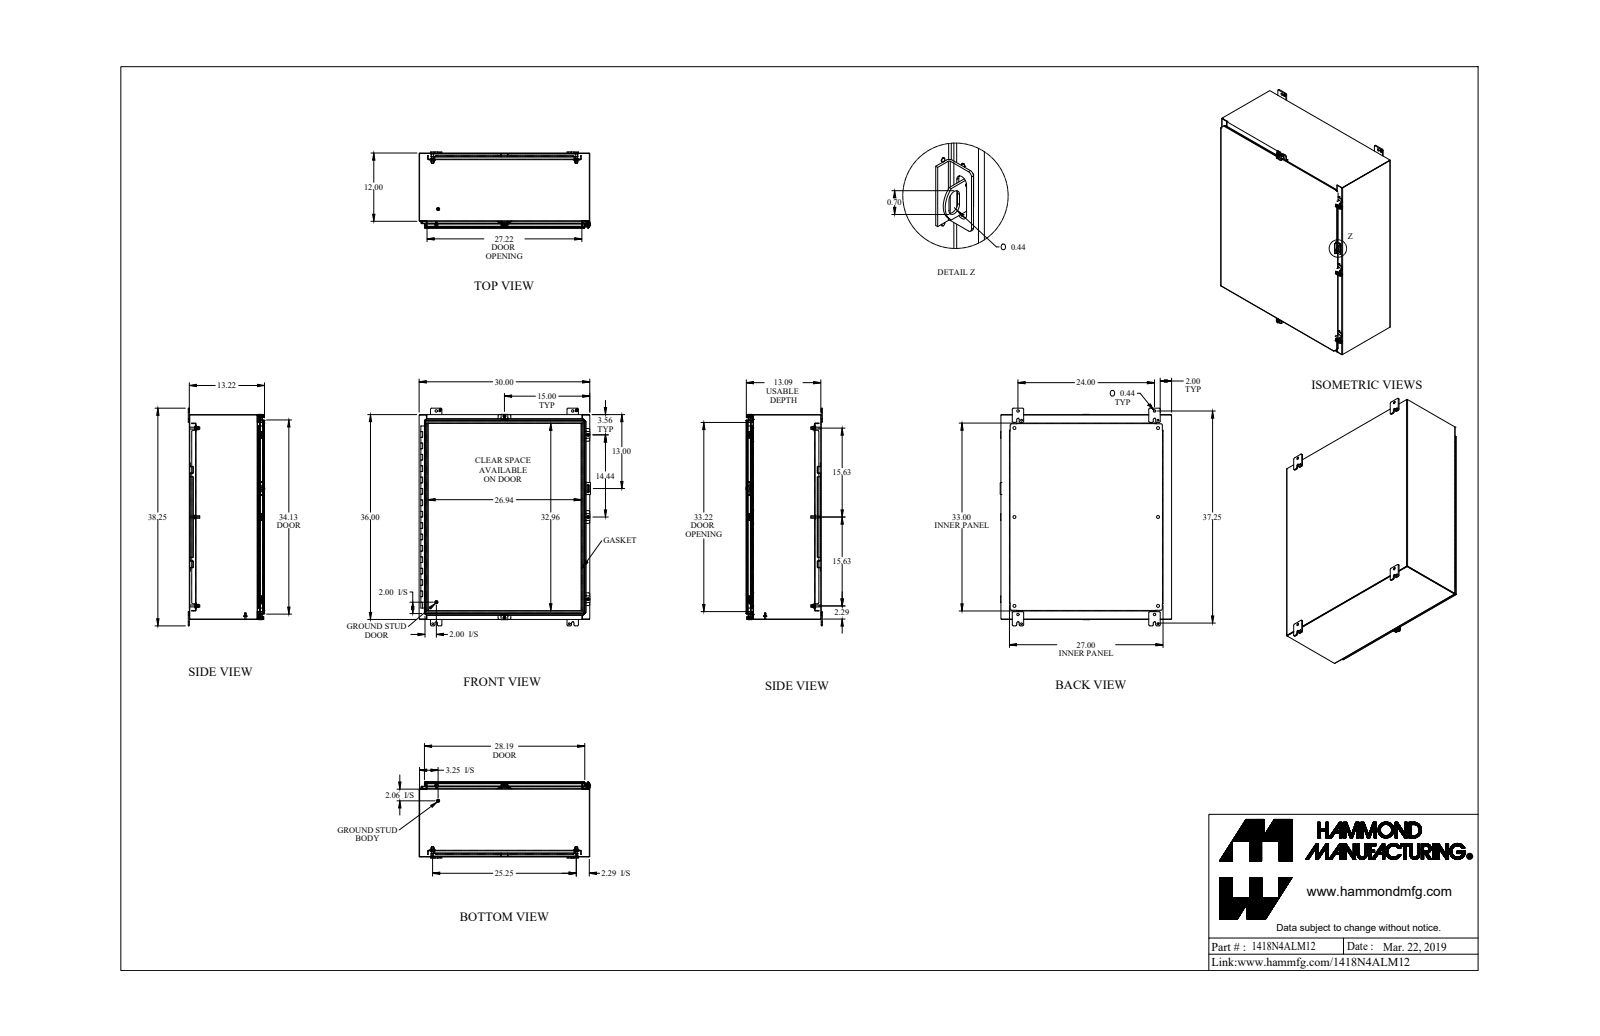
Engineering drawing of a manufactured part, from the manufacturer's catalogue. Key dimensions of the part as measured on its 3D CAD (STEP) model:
Part name (STEP PRODUCT): 1418N4ALM12_Default
STEP written by: SolidWorks 2019 (CONFIG_CONTROL_DESIGN)
Units: inches
Bodies: 53 solids, 1899 faces (1135 planar, 690 cylindrical, 74 other)
Overall size (bounding box): 38.25 × 30.126 × 13.438
Volume: 477.4 in³ · Surface area: 11 012 in²
Round holes (diameter × count): ⌀0.5 ×6, ⌀0.232 ×5, ⌀0.265 ×5, ⌀0.375 ×5, ⌀0.307 ×4, ⌀0.313 ×4, ⌀0.437 ×4, ⌀0.445 ×4, ⌀0.125 ×1, ⌀0.187 ×1
Round bosses / shafts (diameter × count): ⌀0.131 ×14, ⌀0.65 ×6, ⌀0.375 ×6, ⌀0.33 ×6, ⌀0.5 ×5, ⌀0.4 ×5, ⌀0.244 ×5, ⌀1 ×4
Partial cylindrical surfaces — rounded edges, fillets, slot ends (radius × count): R0.25 ×32, R0.05 ×26, R0.15 ×26, R0.188 ×24, R0.04 ×14, R0.041 ×14, R0.121 ×14, R0.122 ×14
Main face-to-face distances: 0.081, 0.1, 13.041, 13.122, 0.095, 13.141, 13.222, 12.046, 11.946, 1.095
Hole centre spacings: 31.25, 3.065, 12.803, 15.625, 21.782, 24, 25.25, 32.756
